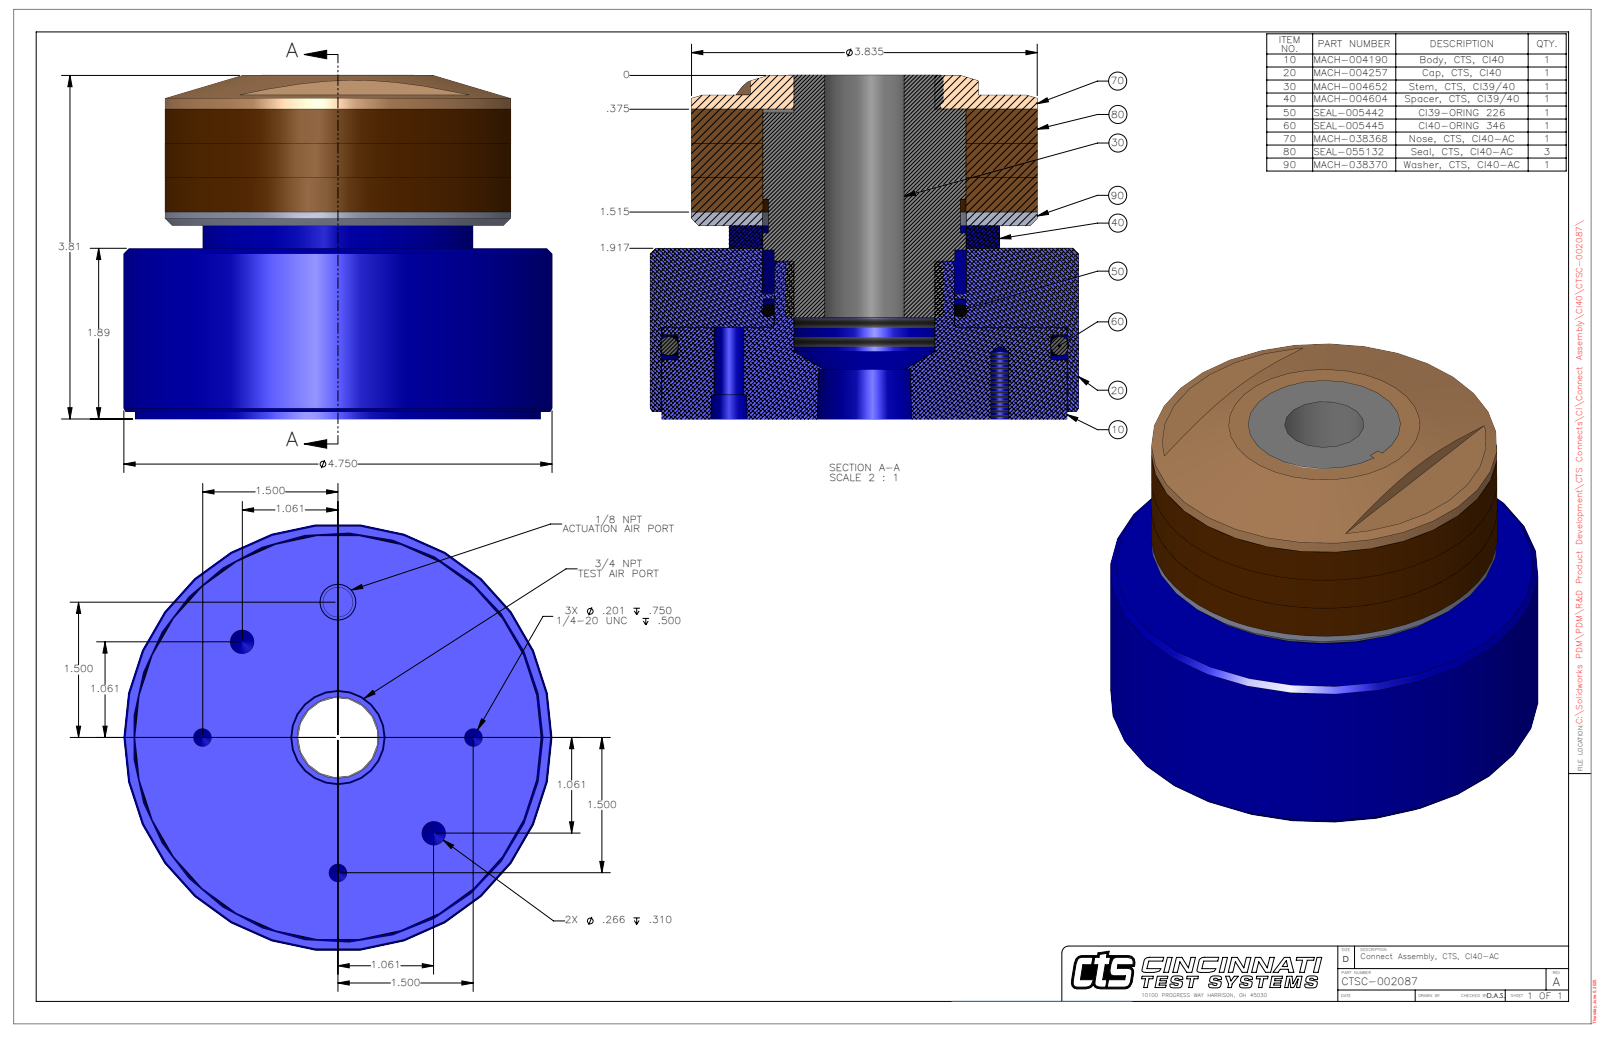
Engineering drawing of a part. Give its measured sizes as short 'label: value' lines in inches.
name: CTSC-002087
written by: SolidWorks 2023 (AUTOMOTIVE_DESIGN)
unit: in
bodies: 1 solid, 94 faces (32 planar, 39 cylindrical, 23 other)
size: 4.75 × 4.75 × 3.813
volume: 50.43 in³; area: 123.9 in²
holes: 3× ⌀0.201, 2× ⌀0.266, 1× ⌀0.332, 1× ⌀0.88, 1× ⌀2.25, 1× ⌀2.26, 1× ⌀2.261, 1× ⌀4.5
bosses: 1× ⌀4.75, 1× ⌀4.492, 1× ⌀3.835, 1× ⌀3, 1× ⌀2.12
rounds: 1× R0.062, 1× R0.781
face distances: 1.893, 2.143, 0.25, 3.591, 1.698, 1.448, 3.813, 1.92, 1.67, 0.222
hole spacings: 1.5, 1.148, 2.121, 2.772, 3
